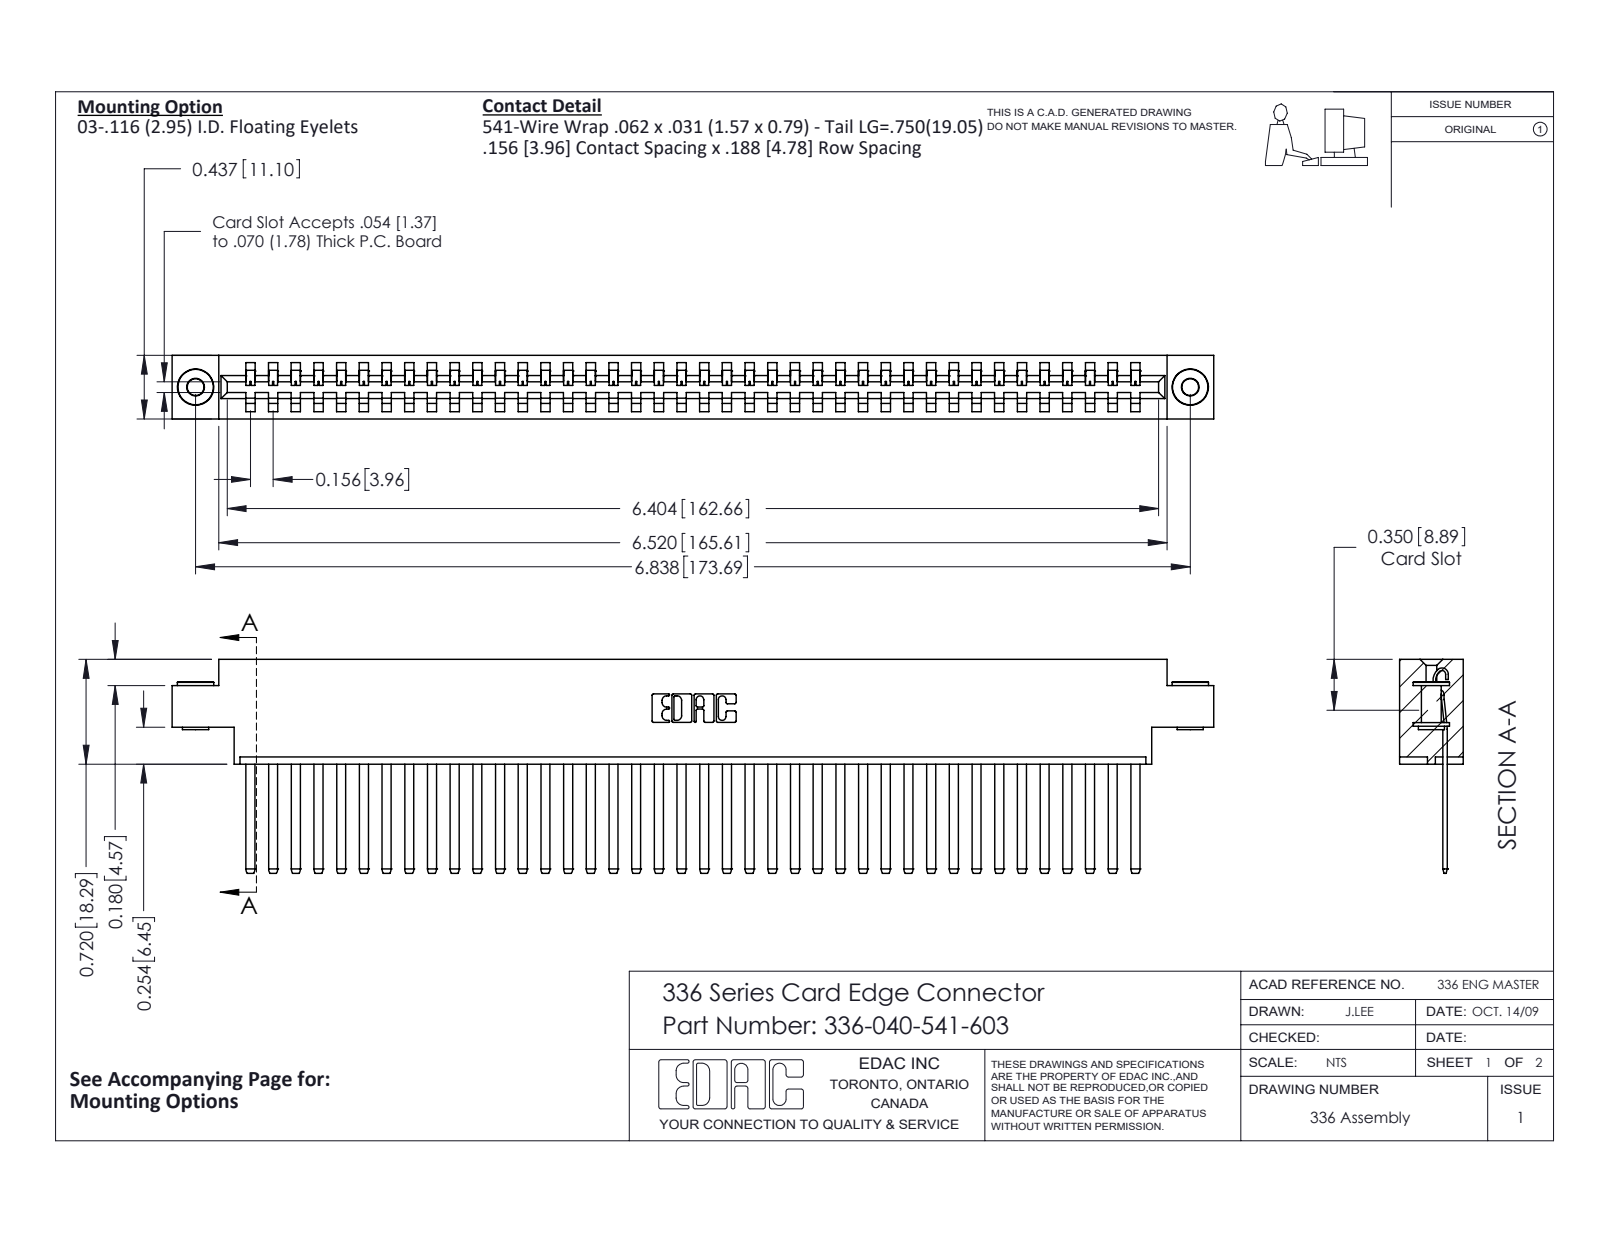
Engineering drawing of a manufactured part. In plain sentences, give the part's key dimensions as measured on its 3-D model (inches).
The part is named "336-040-541-603; 336-290-001_336-290-541; 345-250-002_345-250-002-102; 336 Part_Offset - .156 Dia - TH". Its 3-D file was written by "SolidWorks 2020 (CONFIG_CONTROL_DESIGN)". It is 43 solids with 2156 faces: 1444 planar, 704 cylindrical and 8 other. Overall it measures 7.161 by 1.47 by 0.437 inches. Its volume is 1.615 cubic inches and its surface area 45.09 square inches. Round holes: 2 of diameter 0.116, 2 of diameter 0.156. Round bosses or shafts: 2 of diameter 0.25, 2 of diameter 0.18, 2 of diameter 0.136. Partial cylindrical surfaces (rounded edges, fillets, slot ends): 80 of radius 0.004, 80 of radius 0.056, 22 of radius 0.01, 6 of radius 0.007, 6 of radius 0.031, 3 of radius 0.026, 2 of radius 0.022, 2 of radius 0.04. The main face-to-face distances are 0.437, 0.031, 0.181, 0.328, 0.14, 0.297, 0.109, 0.256, 0.05, 0.387. The hole center spacings are 6.838.
